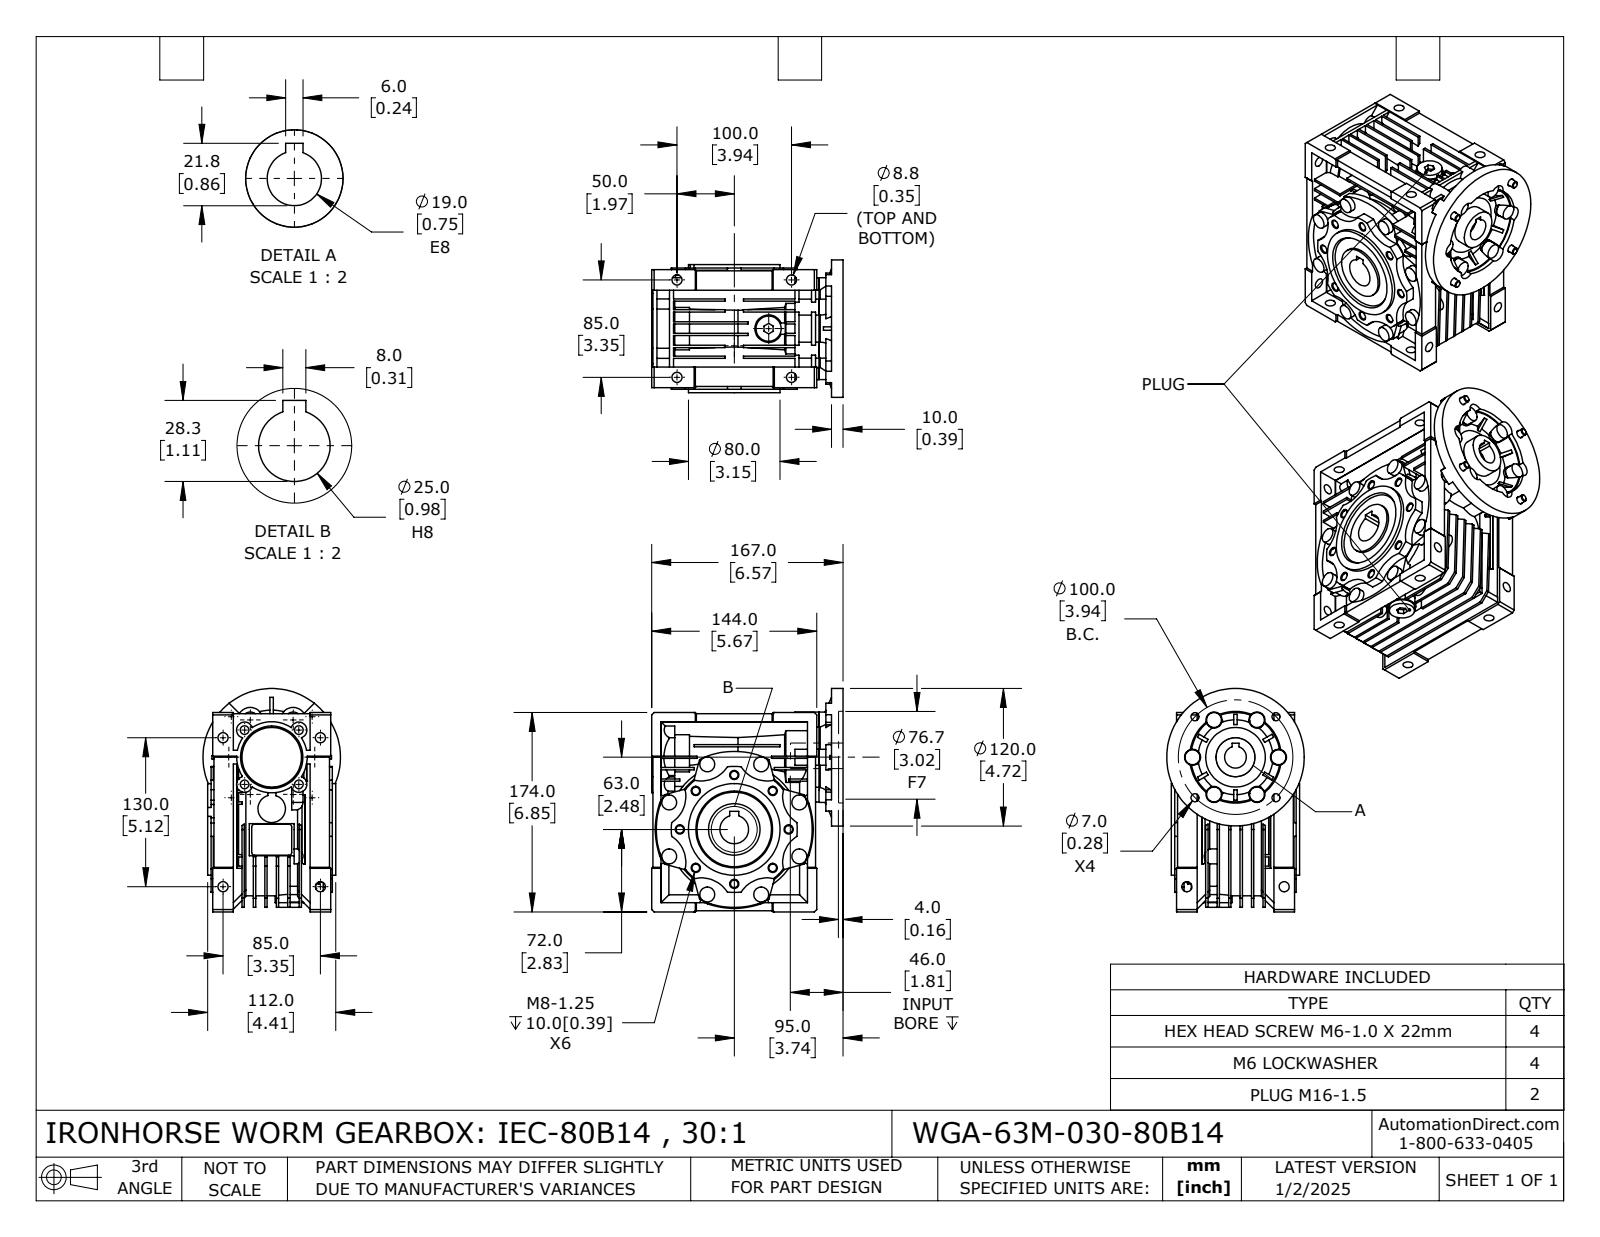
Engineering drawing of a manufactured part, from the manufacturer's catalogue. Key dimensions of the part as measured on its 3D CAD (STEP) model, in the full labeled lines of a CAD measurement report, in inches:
Part name (STEP PRODUCT): WGA-63M-030-80B14
STEP written by: SolidWorks 2024 (CONFIG_CONTROL_DESIGN)
Units: inches
Bodies: 16 solids, 1442 faces (853 planar, 413 cylindrical, 176 other)
Overall size (bounding box): 7.677 × 6.791 × 4.724
Volume: 112.7 in³ · Surface area: 542.9 in²
Round holes (diameter × count): ⌀0.262 ×8, ⌀0.346 ×8, ⌀0.24 ×4, ⌀0.276 ×4, ⌀0.298 ×4, ⌀0.571 ×2, ⌀0.748 ×1, ⌀0.787 ×1, ⌀0.984 ×1, ⌀1.339 ×1, ⌀1.457 ×1, ⌀1.772 ×1
Round bosses / shafts (diameter × count): ⌀0.512 ×14, ⌀0.551 ×6, ⌀0.48 ×4, ⌀0.236 ×4, ⌀0.945 ×3, ⌀0.866 ×2, ⌀0.622 ×2, ⌀0.539 ×2
Partial cylindrical surfaces — rounded edges, fillets, slot ends (radius × count): R0.276 ×10, R1.063 ×8, R0.275 ×6, R0.433 ×6, R0.098 ×4, R0.329 ×1, R1.161 ×1, R1.201 ×1
Main face-to-face distances: 0.394, 0.315, 0.787, 0.079, 1.181, 0.709, 0.472, 0.276, 1.575, 0.039
Hole centre spacings: 1.431, 1.87, 2.37, 2.645, 3.456, 0.65, 1.319, 1.865
